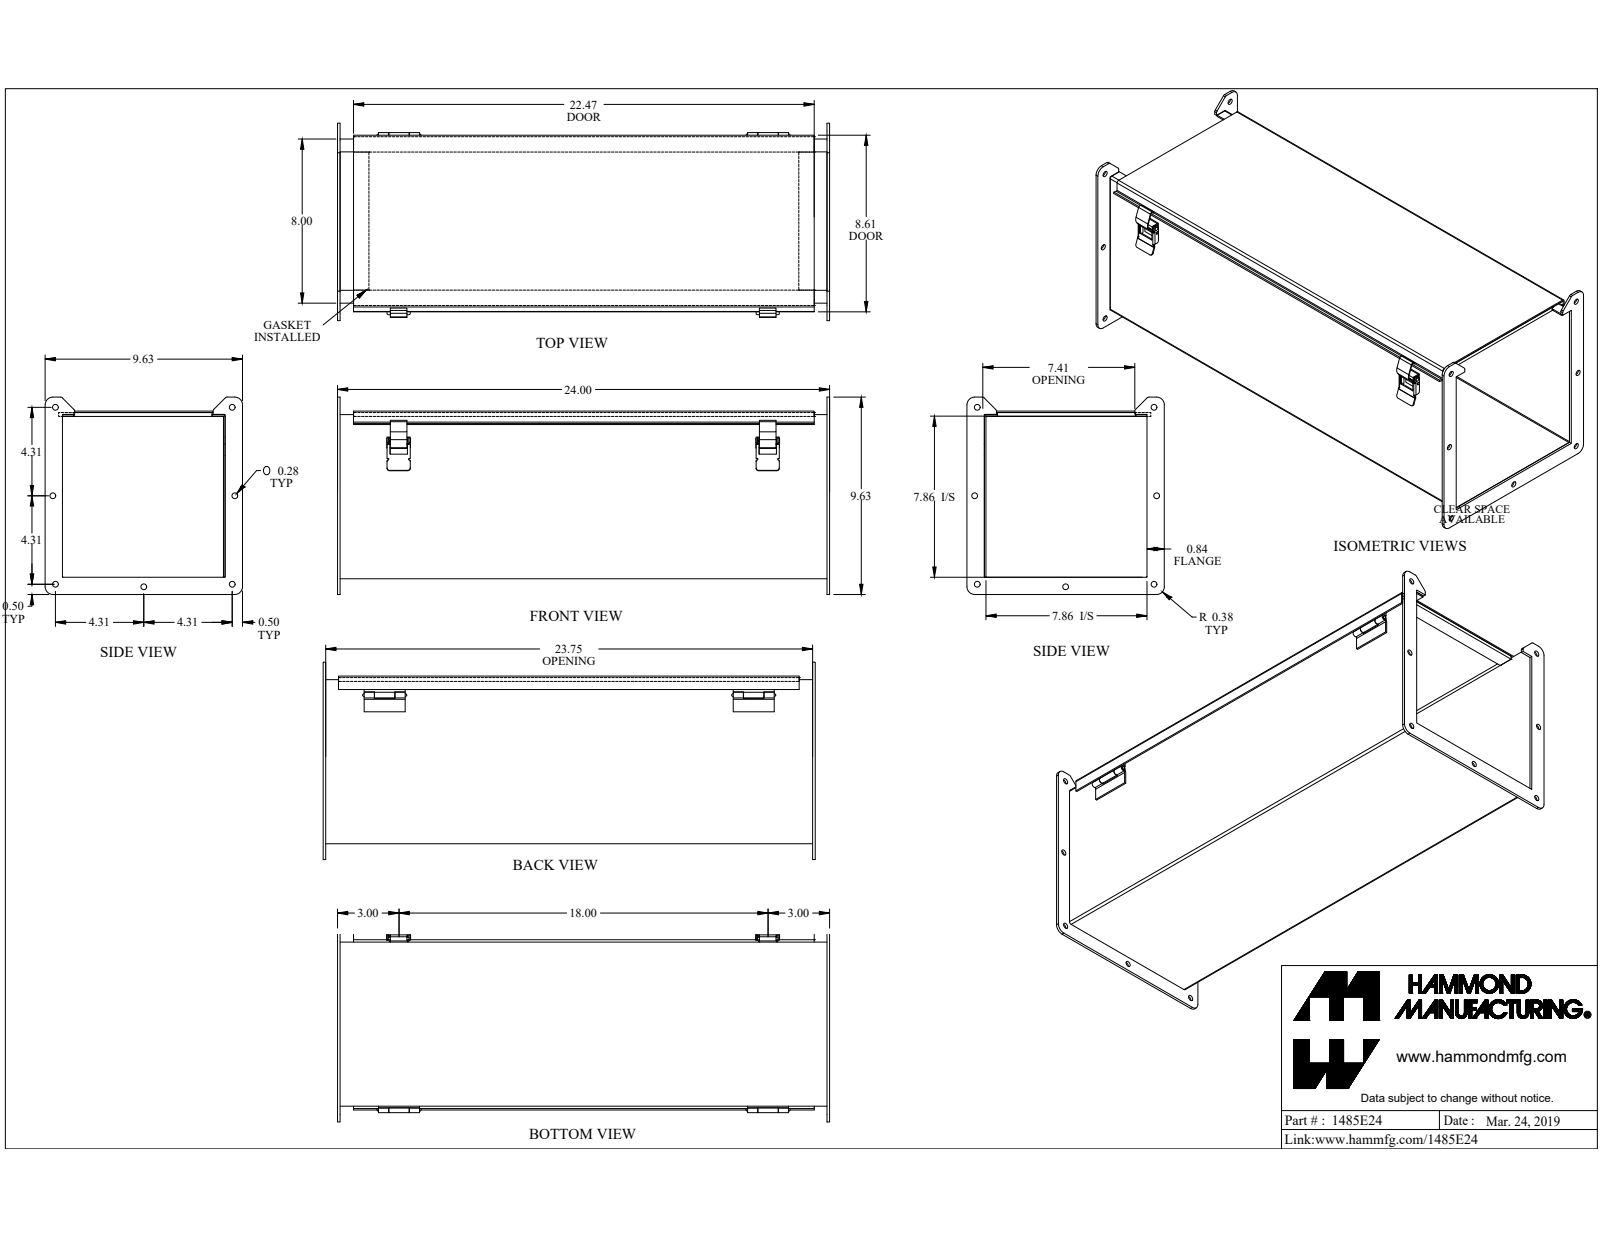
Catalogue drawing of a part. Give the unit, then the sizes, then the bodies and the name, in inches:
Units: inches
Overall size (bounding box): 24 × 9.625 × 9.625
Round holes (diameter × count): ⌀0.281 ×7, ⌀0.125 ×1, ⌀0.13 ×1, ⌀0.164 ×1
Round bosses / shafts (diameter × count): ⌀0.187 ×2, ⌀0.275 ×1, ⌀0.156 ×1, ⌀0.125 ×1, ⌀0.125 ×1
Partial cylindrical surfaces — rounded edges, fillets, slot ends (radius × count): R0.016 ×13, R0.125 ×9, R0.036 ×7, R0.108 ×7, R0.035 ×5, R0.039 ×5, R0.076 ×5, R0.015 ×4
Main face-to-face distances: 0.072, 7.928, 8.1, 8, 7.856, 8.028, 8.172, 0.172, 0.125, 23.875
Hole centre spacings: 8.625, 4.314, 4.315, 9.755, 9.755, 6.276, 12.197, 0.285
Volume: 73.22 in³ · Surface area: 1 885 in²
Bodies: 20 solids, 416 faces (250 planar, 162 cylindrical, 4 other)
Part name (STEP PRODUCT): 1485E24
STEP written by: SolidWorks 2019 (CONFIG_CONTROL_DESIGN)
